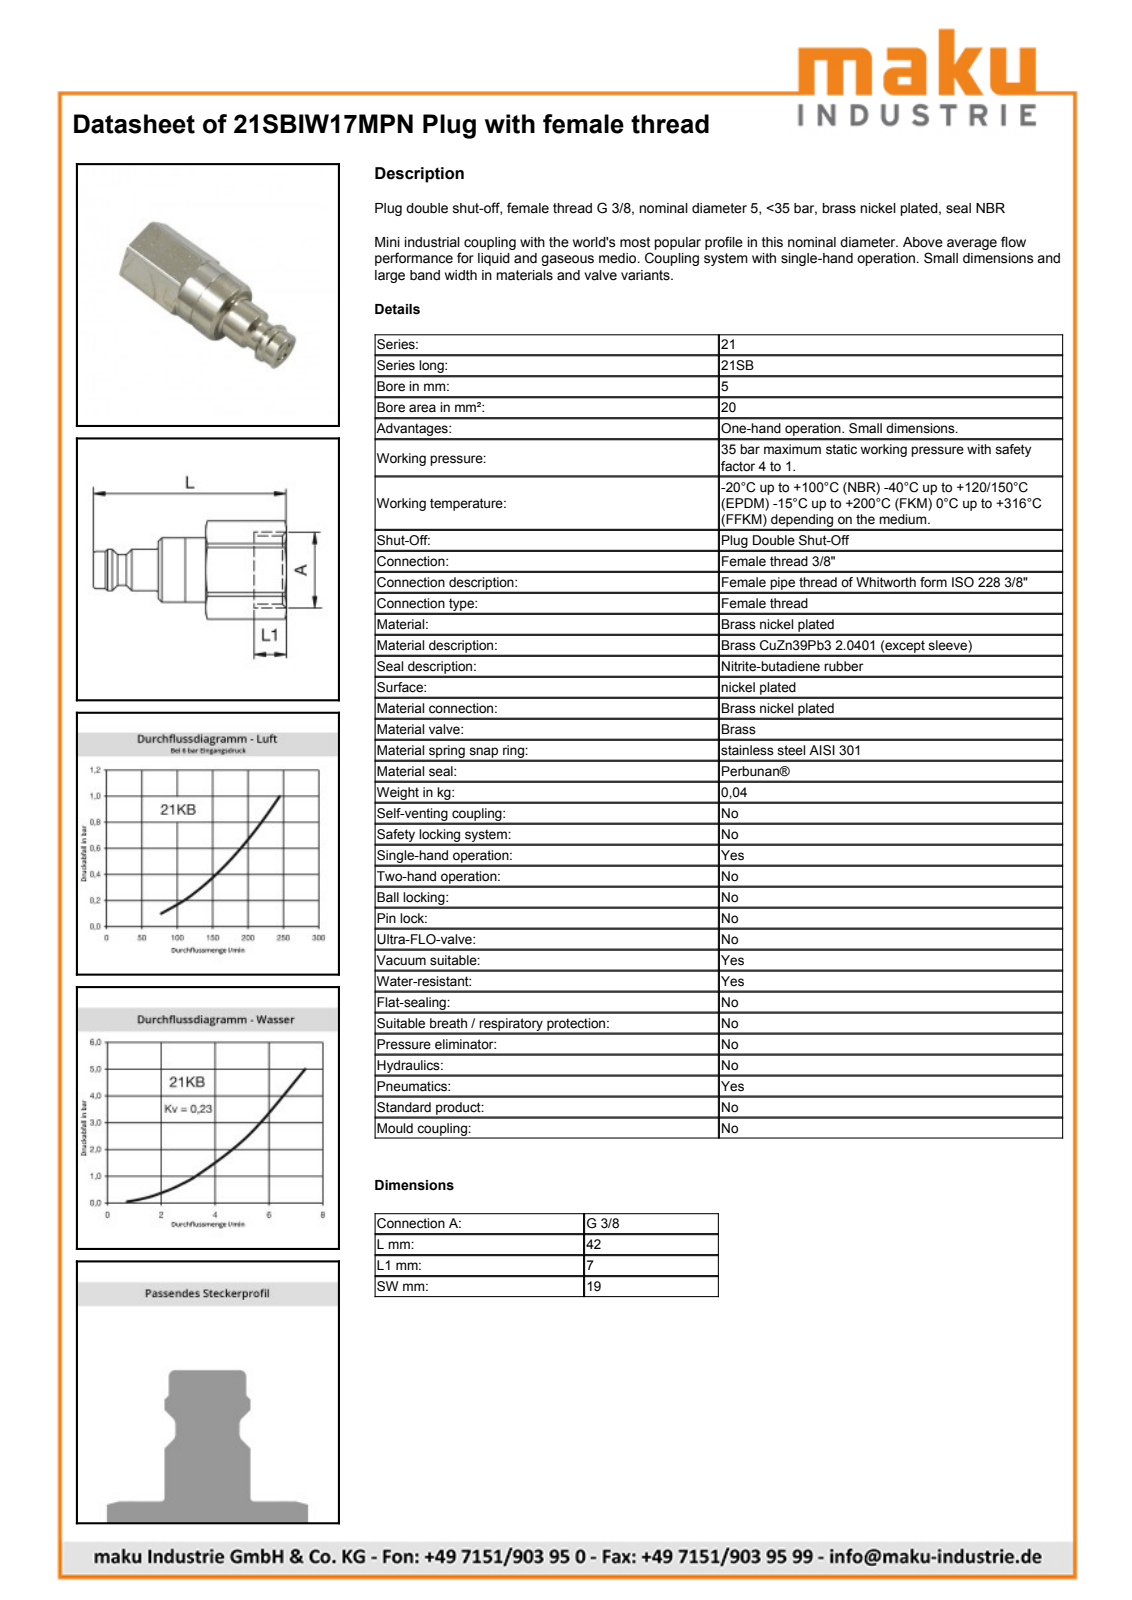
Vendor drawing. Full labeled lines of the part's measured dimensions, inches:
Part name (STEP PRODUCT): D113095
STEP written by: Autodesk Inventor 2013 (AUTOMOTIVE_DESIGN)
Units: inches
Bodies: 1 solid, 54 faces (11 planar, 17 cylindrical, 26 other)
Overall size (bounding box): 1.654 × 0.833 × 0.809
Volume: 0.377 in³ · Surface area: 5.033 in²
Round holes (diameter × count): ⌀0.283 ×1, ⌀0.451 ×1, ⌀0.589 ×1
Round bosses / shafts (diameter × count): ⌀0.551 ×1, ⌀0.433 ×1, ⌀0.354 ×1, ⌀0.319 ×1, ⌀0.262 ×1, ⌀0.249 ×1
Partial cylindrical surfaces — rounded edges, fillets, slot ends (radius × count): R0.421 ×1
Main face-to-face distances: 0.748, 0.337, 0.691, 0.354, 0.407, 0.744, 1.098, 0.555, 0.963, 1.299
